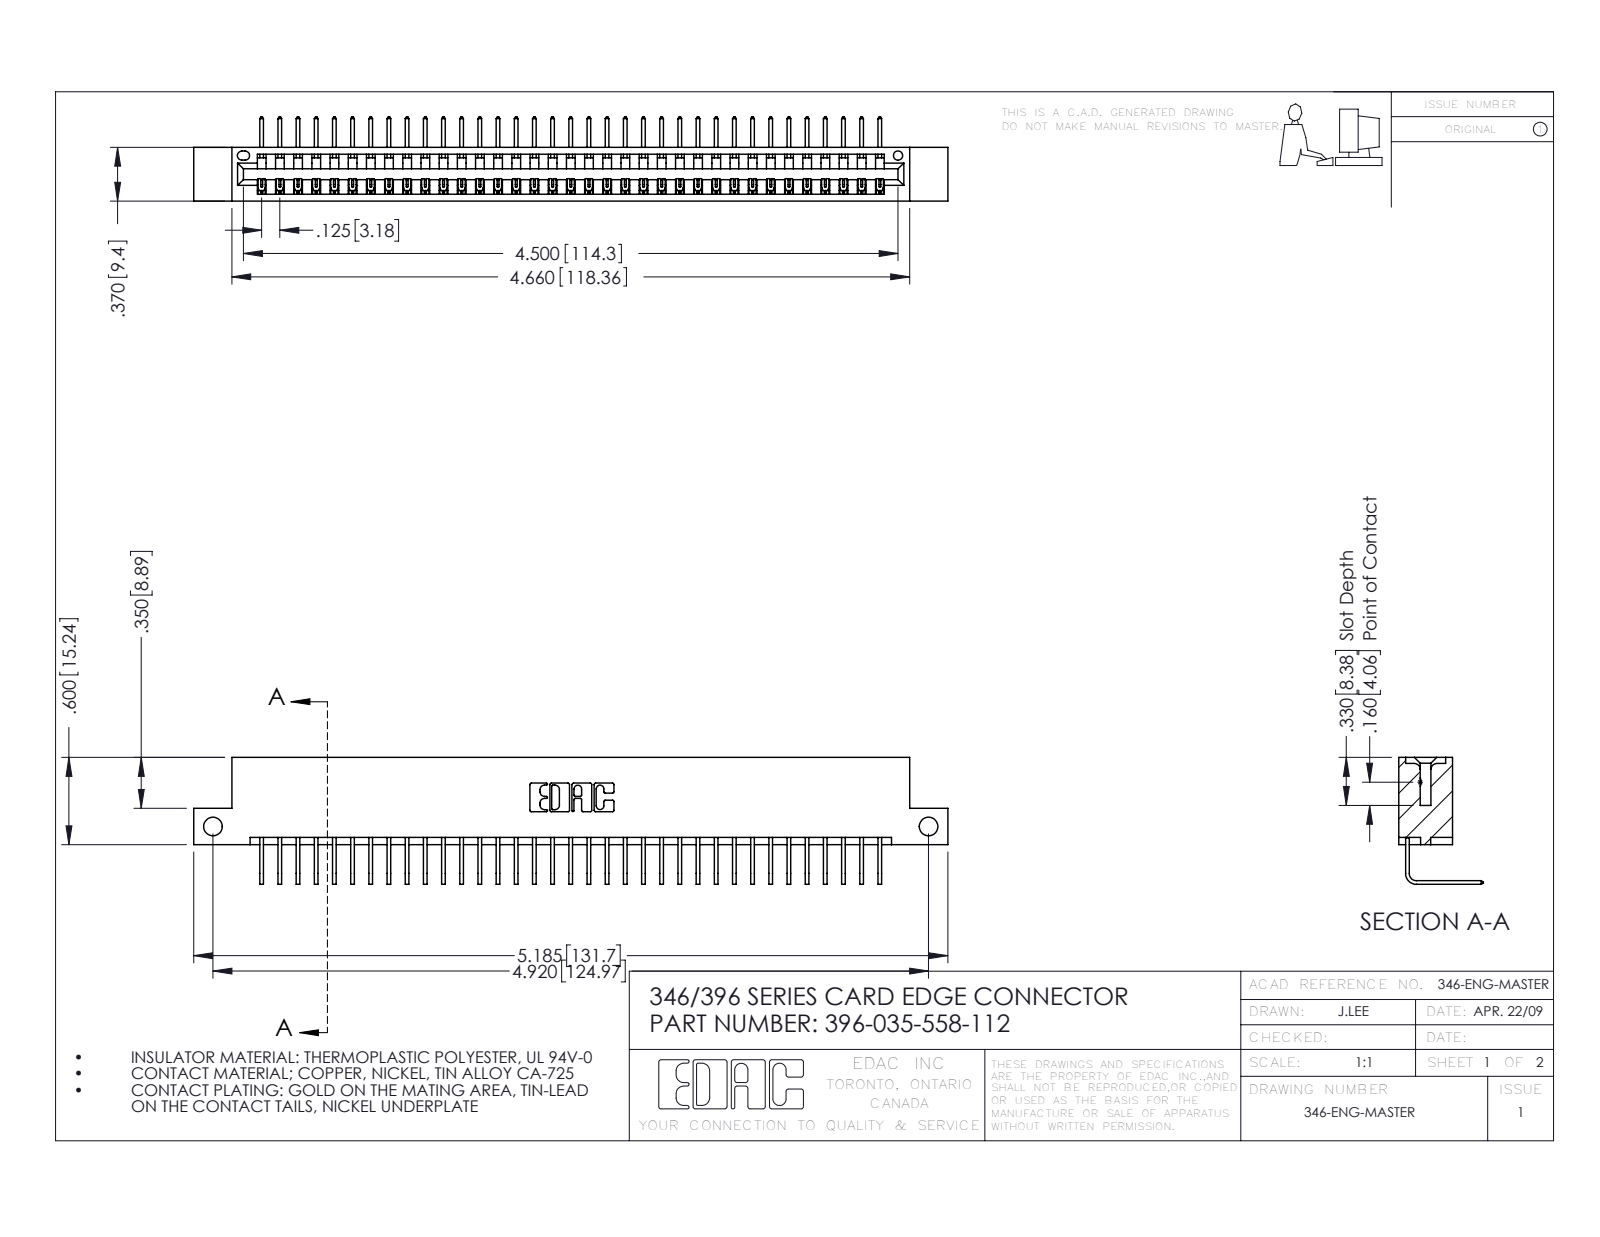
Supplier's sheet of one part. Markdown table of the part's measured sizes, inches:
| quantity | value |
| --- | --- |
| part name | 396-035-558-112; 346 Part_Flush Mounting Lugs - Side Mount; 345-292-001_558 Tail - 2 |
| STEP written by | SolidWorks 2016 (CONFIG_CONTROL_DESIGN) |
| units | inches |
| bodies | 36 solids, 2222 faces (1546 planar, 676 cylindrical, 0 other) |
| overall size | 5.185 × 0.873 × 0.58 |
| volume | 0.768 in³ |
| surface area | 25.12 in² |
| round holes (diameter × count) | 0.128 × 2, 0.064 × 1 |
| partial cylindrical surfaces (radius × count) | 0.006 × 70, 0.01 × 22, 0.007 × 6, 0.031 × 6, 0.026 × 3, 0.031 × 2, 0.04 × 2, 0.014 × 1 |
| main face-to-face distances | 0.322, 0.048, 0.37, 0.25, 0.298, 0.025, 0.072, 0.148, 0.222, 0.1 |
| hole center spacings | 4.92 |
